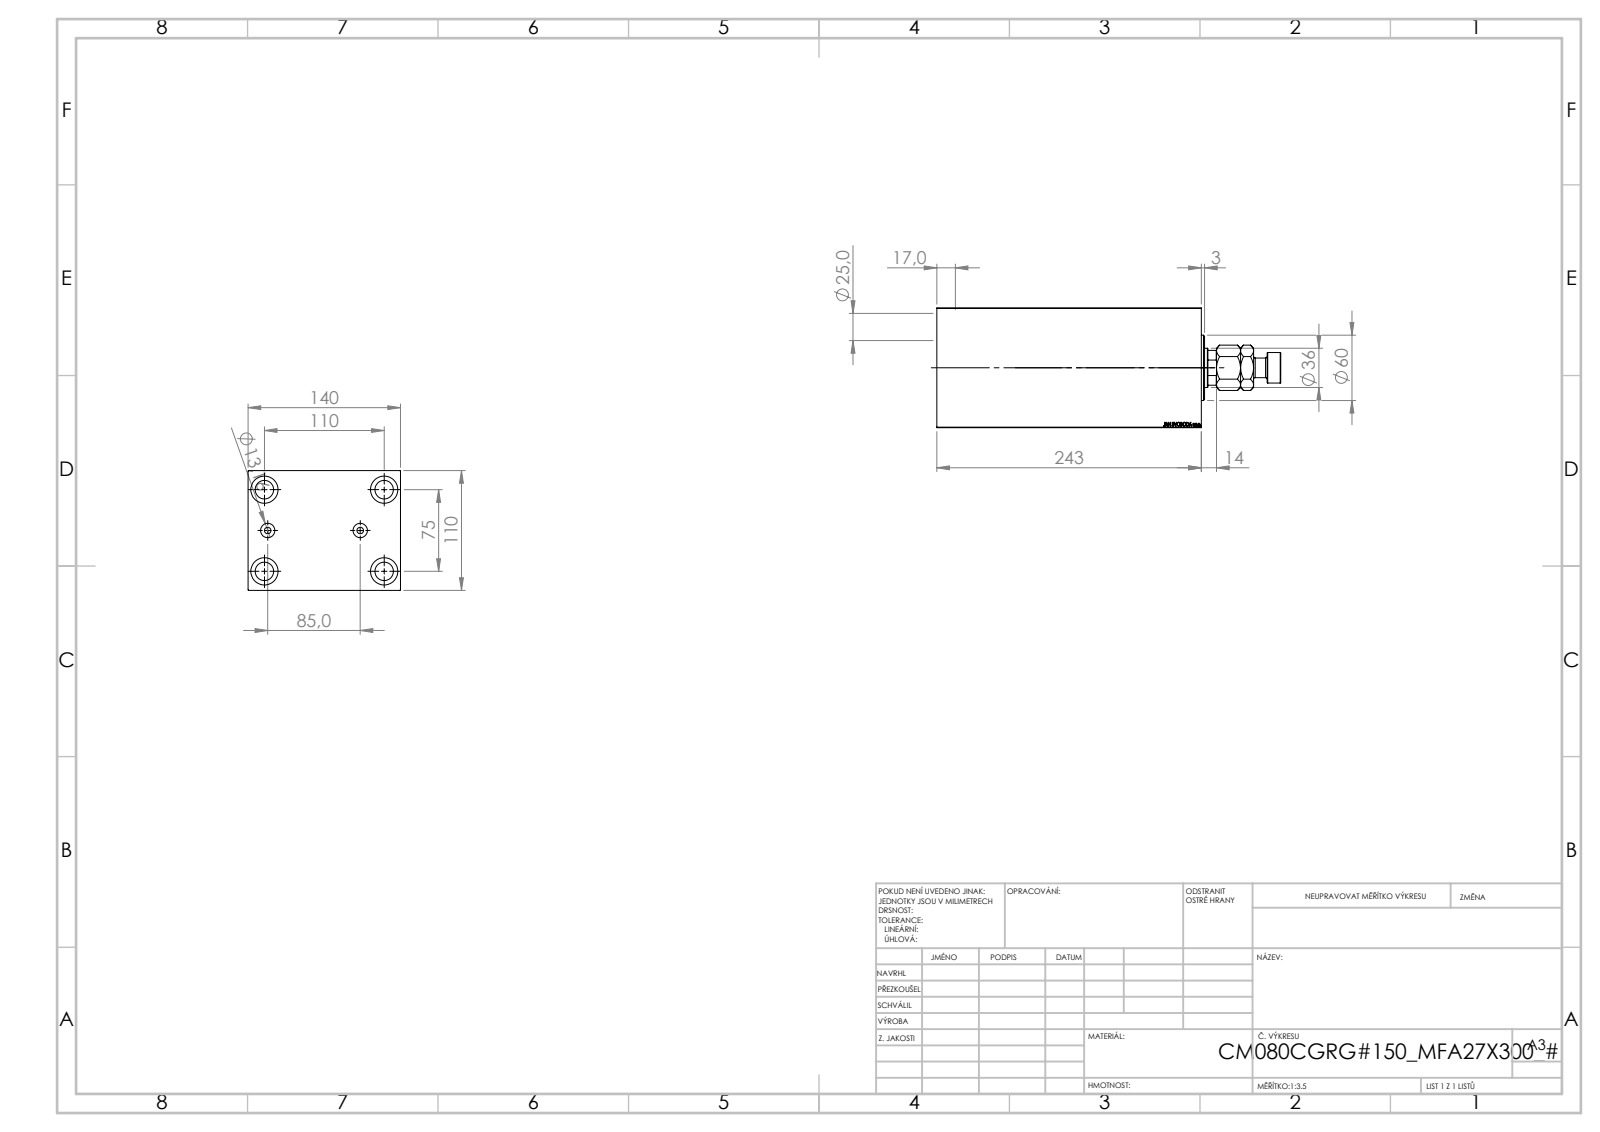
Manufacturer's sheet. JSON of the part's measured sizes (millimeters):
{"part_name": "V450CM_C_Body; V450CM_VC_B; V450CM_C_VCP; MFA", "step_written_by": "SolidWorks 2019 (CONFIG_CONTROL_DESIGN)", "units": "millimeters", "bodies": {"solids": 4, "faces": 915, "planar": 427, "cylindrical": 62, "other": 426}, "overall_size": [316, 140, 110], "volume_mm3": 2918000, "surface_area_mm2": 320031, "round_holes": [[17, 4], [25, 4], [6, 2], [13.16, 2], [25.5, 1], [36, 1], [39.5, 1], [80, 1], [82, 1], [87, 1]], "round_bosses_or_shafts": [[60, 1], [28, 1], [18, 1]], "partial_cylinders_radius": [[17.5, 1]], "face_to_face_distances": [110, 140, 243, 183.25, 59.75, 233, 10, 83, 173.25, 160], "hole_center_spacings": [39.53, 66.57, 104.46, 42.5, 75, 110, 133.14, 85]}
